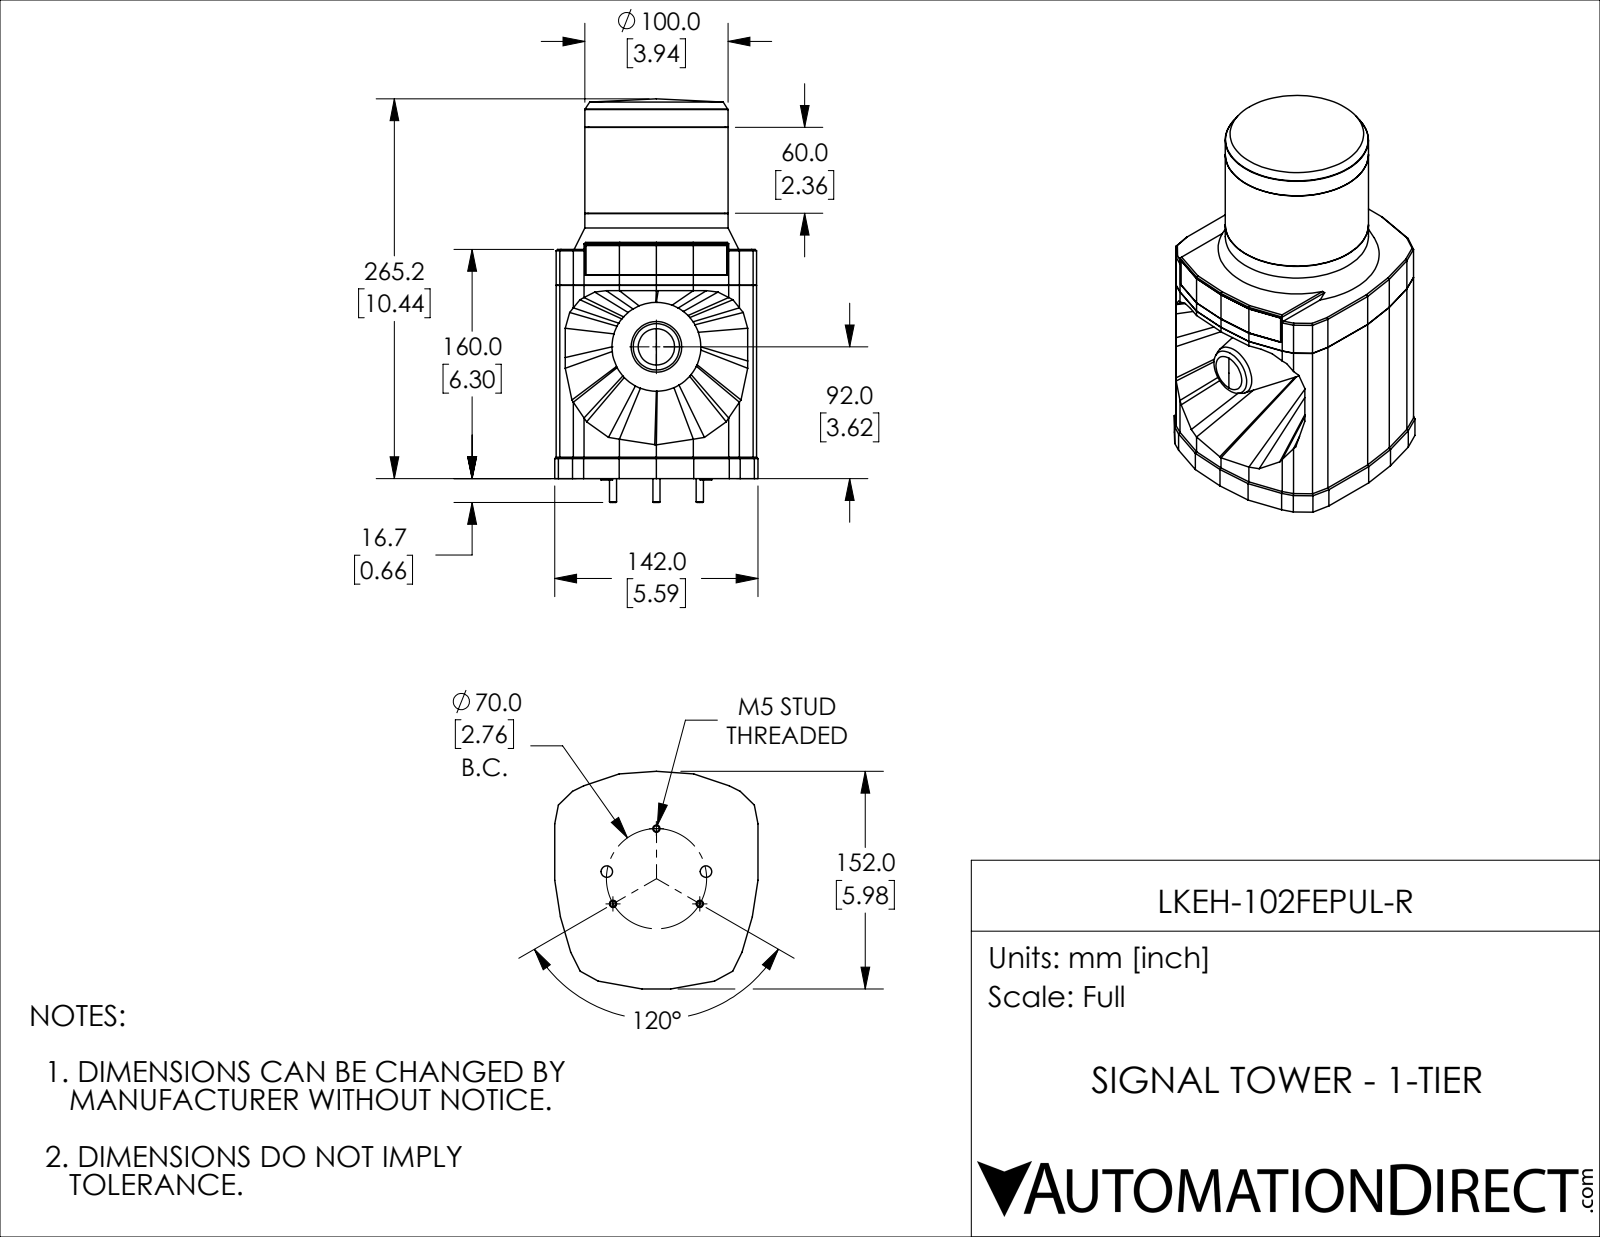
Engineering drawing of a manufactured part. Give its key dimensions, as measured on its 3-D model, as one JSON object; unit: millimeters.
{"part_name": "LKEH-102FEPUL-R", "step_written_by": "SolidWorks 2018 (AUTOMOTIVE_DESIGN)", "units": "millimeters", "bodies": {"solids": 1, "faces": 262, "planar": 180, "cylindrical": 20, "other": 62}, "overall_size": [281.9, 152, 142], "volume_mm3": 3327000, "surface_area_mm2": 175700, "round_bosses_or_shafts": [[5, 3], [8, 2], [100, 1], [95.6, 1]], "face_to_face_distances": [1, 140, 160, 165, 5, 141, 50.1, 1, 1, 245.3]}
